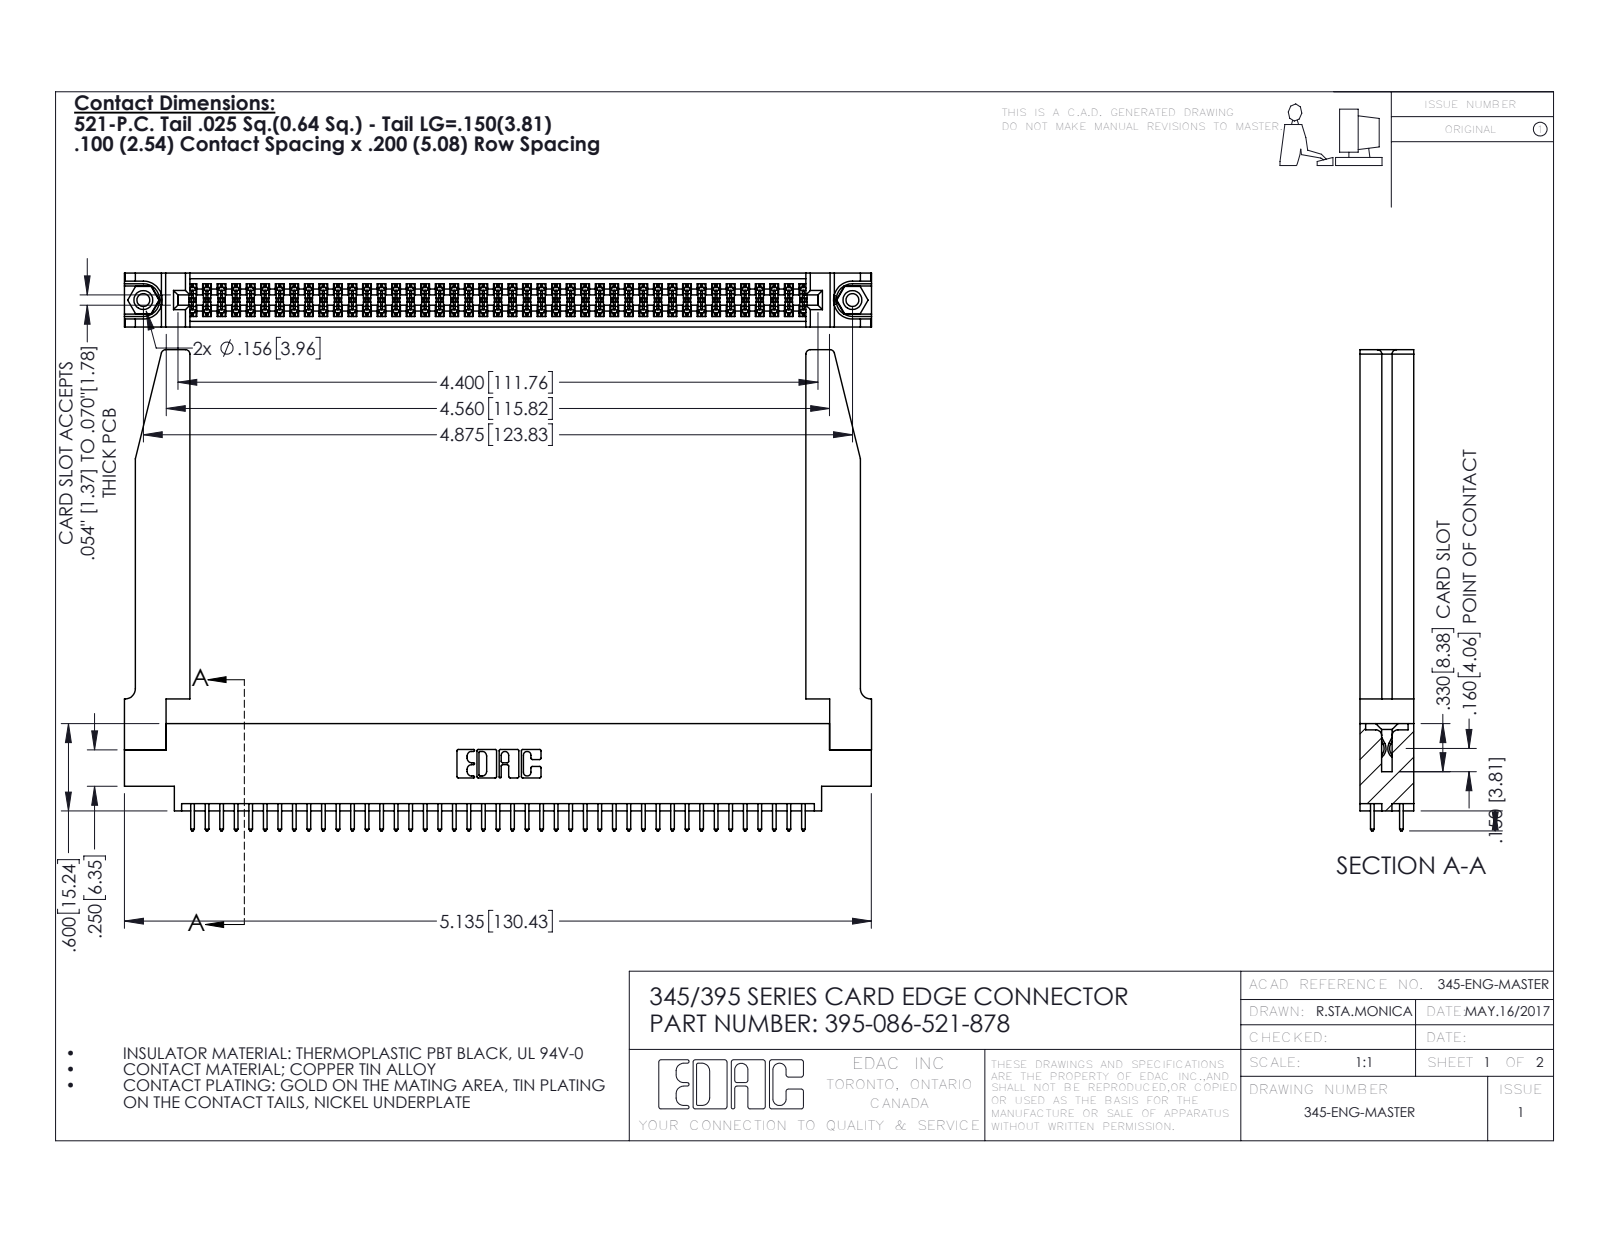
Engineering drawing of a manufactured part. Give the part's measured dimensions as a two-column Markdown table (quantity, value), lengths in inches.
| quantity | value |
| --- | --- |
| part name | 345 Part_0.170 Offset - 0.156 Dia-TH; 345-292-001_345-293-121; 345-220-078_345-220-078; 395-086-521-878 (+1 more) |
| STEP written by | SolidWorks 2016 (CONFIG_CONTROL_DESIGN) |
| units | inches |
| bodies | 91 solids, 4664 faces (3064 planar, 1548 cylindrical, 52 other) |
| overall size | 5.136 × 3.307 × 0.37 |
| volume | 1.239 in³ |
| surface area | 39.21 in² |
| round holes (diameter × count) | 0.089 × 2, 0.125 × 2, 0.156 × 2, 0.064 × 1 |
| round bosses / shafts (diameter × count) | 0.155 × 2 |
| partial cylindrical surfaces (radius × count) | 0.006 × 129, 0.01 × 86, 0.01 × 22, 0.03 × 8, 0.007 × 6, 0.031 × 6, 0.026 × 3, 0.014 × 2 |
| main face-to-face distances | 0.37, 0.072, 0.298, 0.098, 0.272, 0.025, 0.2, 0.225, 0.175, 0.148 |
| hole center spacings | 0.27, 4.639, 4.875 |
